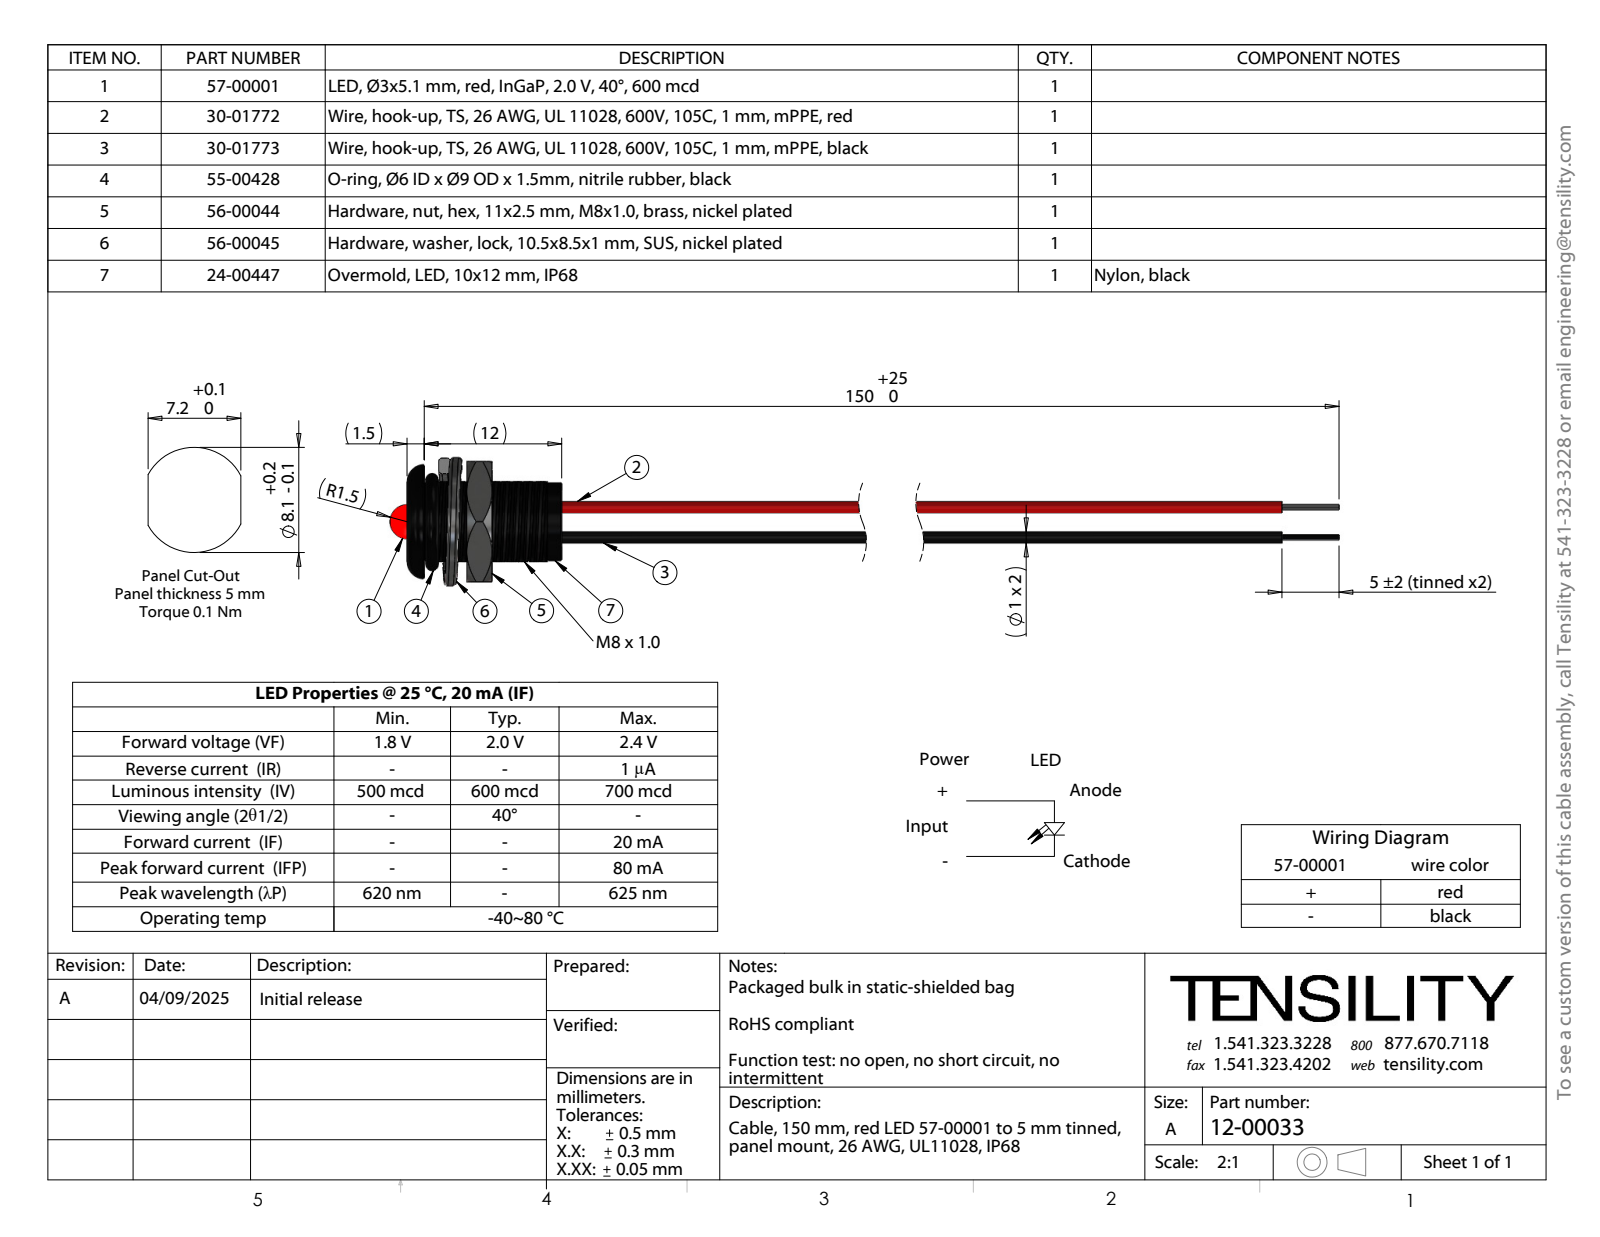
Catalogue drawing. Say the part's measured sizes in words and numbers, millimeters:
The part is named "56-00044; 56-00045_Split washer; 55-00428; 57-00001_trimmed leads (+4 more)". Its 3-D file was written by "SolidWorks 2021 (CONFIG_CONTROL_DESIGN)". It is 57 solids with 555 faces: 186 planar, 246 cylindrical and 123 other. Overall it measures 169.99 by 12.12 by 11.21 millimeters. Its volume is 1 005 cubic millimeters and its surface area 5 908 square millimeters. Round holes: 2 of diameter 1. Round bosses or shafts: 2 of diameter 1, 2 of diameter 0.5, 1 of diameter 6.8, 1 of diameter 3. Partial cylindrical surfaces (rounded edges, fillets, slot ends): 1 of radius 3.48, 1 of radius 4. The main face-to-face distances are 1.5, 13.5, 12, 10.5, 5.21, 3.71, 8.29, 7.41, 5.91, 2.2. The hole center spacings are 0.36, 0.38, 0.33, 2.48, 2.52, 2.43, 2.44, 2.56.
